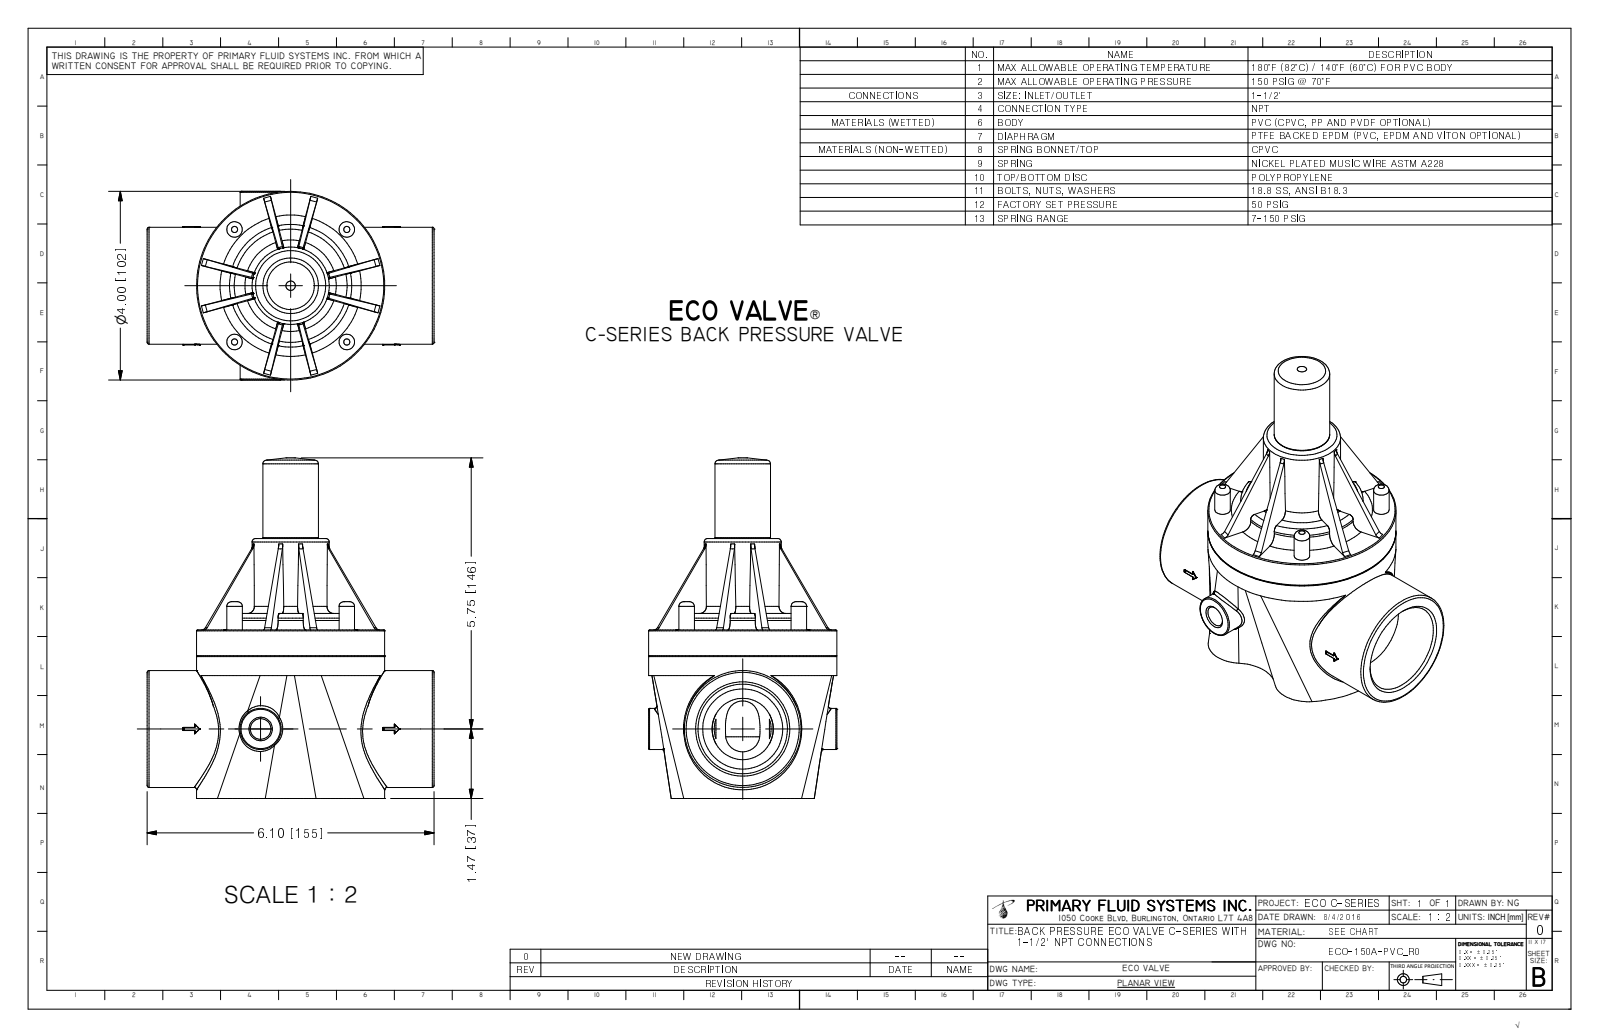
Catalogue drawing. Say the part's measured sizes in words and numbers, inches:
The part is named "ECO-150A-PVC_R0". Its 3-D file was written by "Autodesk Inventor 2009 (AUTOMOTIVE_DESIGN)". It is 1 solid with 424 faces: 173 planar, 89 cylindrical and 162 other. Overall it measures 7.222 by 6.1 by 4 inches. Its volume is 48.99 cubic inches and its surface area 186.4 square inches. Round holes: 4 of diameter 0.23, 1 of diameter 0.437, 1 of diameter 1.7. Round bosses or shafts: 4 of diameter 0.4, 4 of diameter 0.33, 4 of diameter 0.256, 1 of diameter 4, 1 of diameter 2.6, 1 of diameter 2.48, 1 of diameter 1.64, 1 of diameter 1.18. Partial cylindrical surfaces (rounded edges, fillets, slot ends): 14 of radius 0.1, 4 of radius 0.05, 4 of radius 0.128, 4 of radius 0.225, 1 of radius 0.15, 1 of radius 0.65, 1 of radius 0.875, 1 of radius 1.25. The main face-to-face distances are 3.572, 2.05, 0.35, 1.7, 4.4, 0.45, 3.122, 3.007, 2.557, 0.565. The hole center spacings are 2.386, 3.375.
